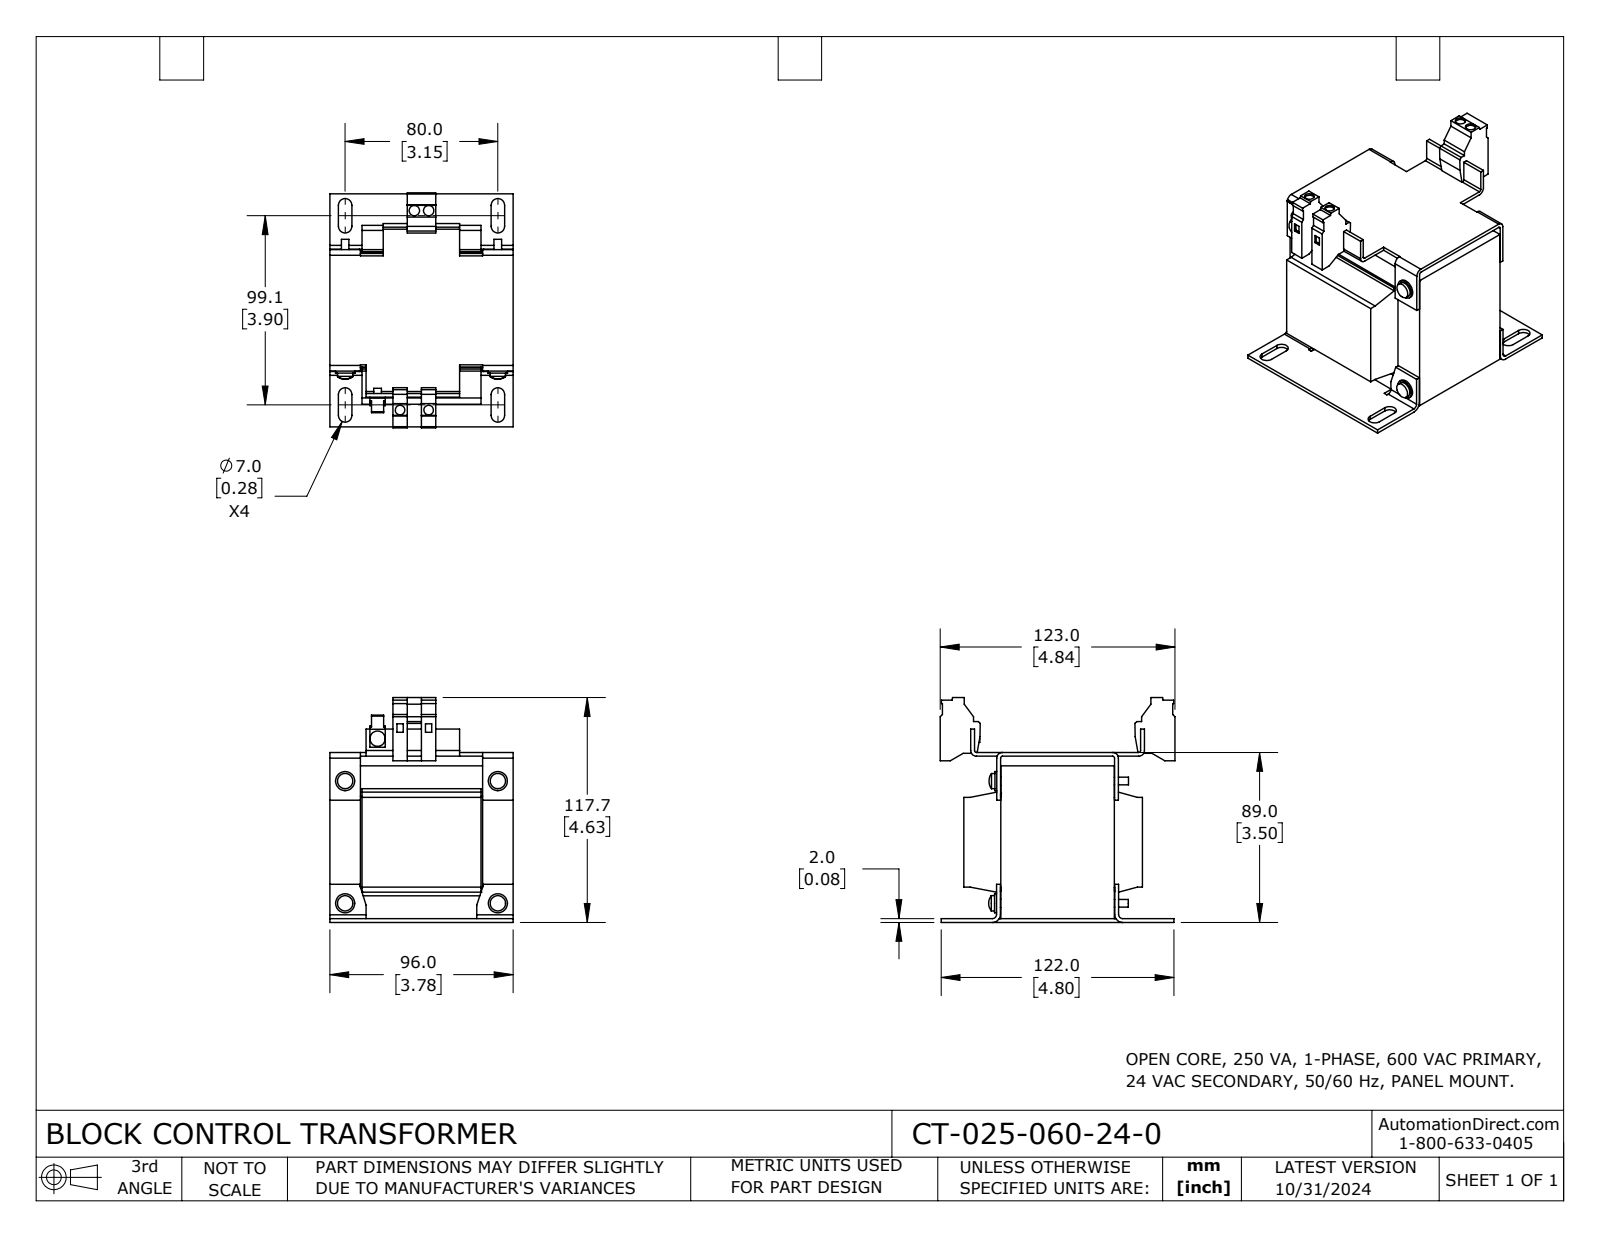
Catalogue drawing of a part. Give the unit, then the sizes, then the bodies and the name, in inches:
Units: inches
Overall size (bounding box): 4.843 × 4.634 × 3.78
Round holes (diameter × count): ⌀0.197 ×2, ⌀0.213 ×2
Round bosses / shafts (diameter × count): ⌀0.315 ×5, ⌀0.157 ×5, ⌀0.394 ×4, ⌀0.177 ×4
Partial cylindrical surfaces — rounded edges, fillets, slot ends (radius × count): R0.138 ×8, R0.039 ×4, R0.118 ×4, R0.079 ×2, R0.157 ×2
Main face-to-face distances: 0.079, 3.425, 3.15, 0.63, 0.661, 3.118, 2.52, 3.504, 3.346, 0.197
Hole centre spacings: 4.121, 0.295, 0.591, 4.11, 4.152
Volume: 37.37 in³ · Surface area: 163.7 in²
Bodies: 1 solid, 330 faces (241 planar, 85 cylindrical, 4 other)
Part name (STEP PRODUCT): CT-025-060-24-0
STEP written by: SolidWorks 2023 (CONFIG_CONTROL_DESIGN)
